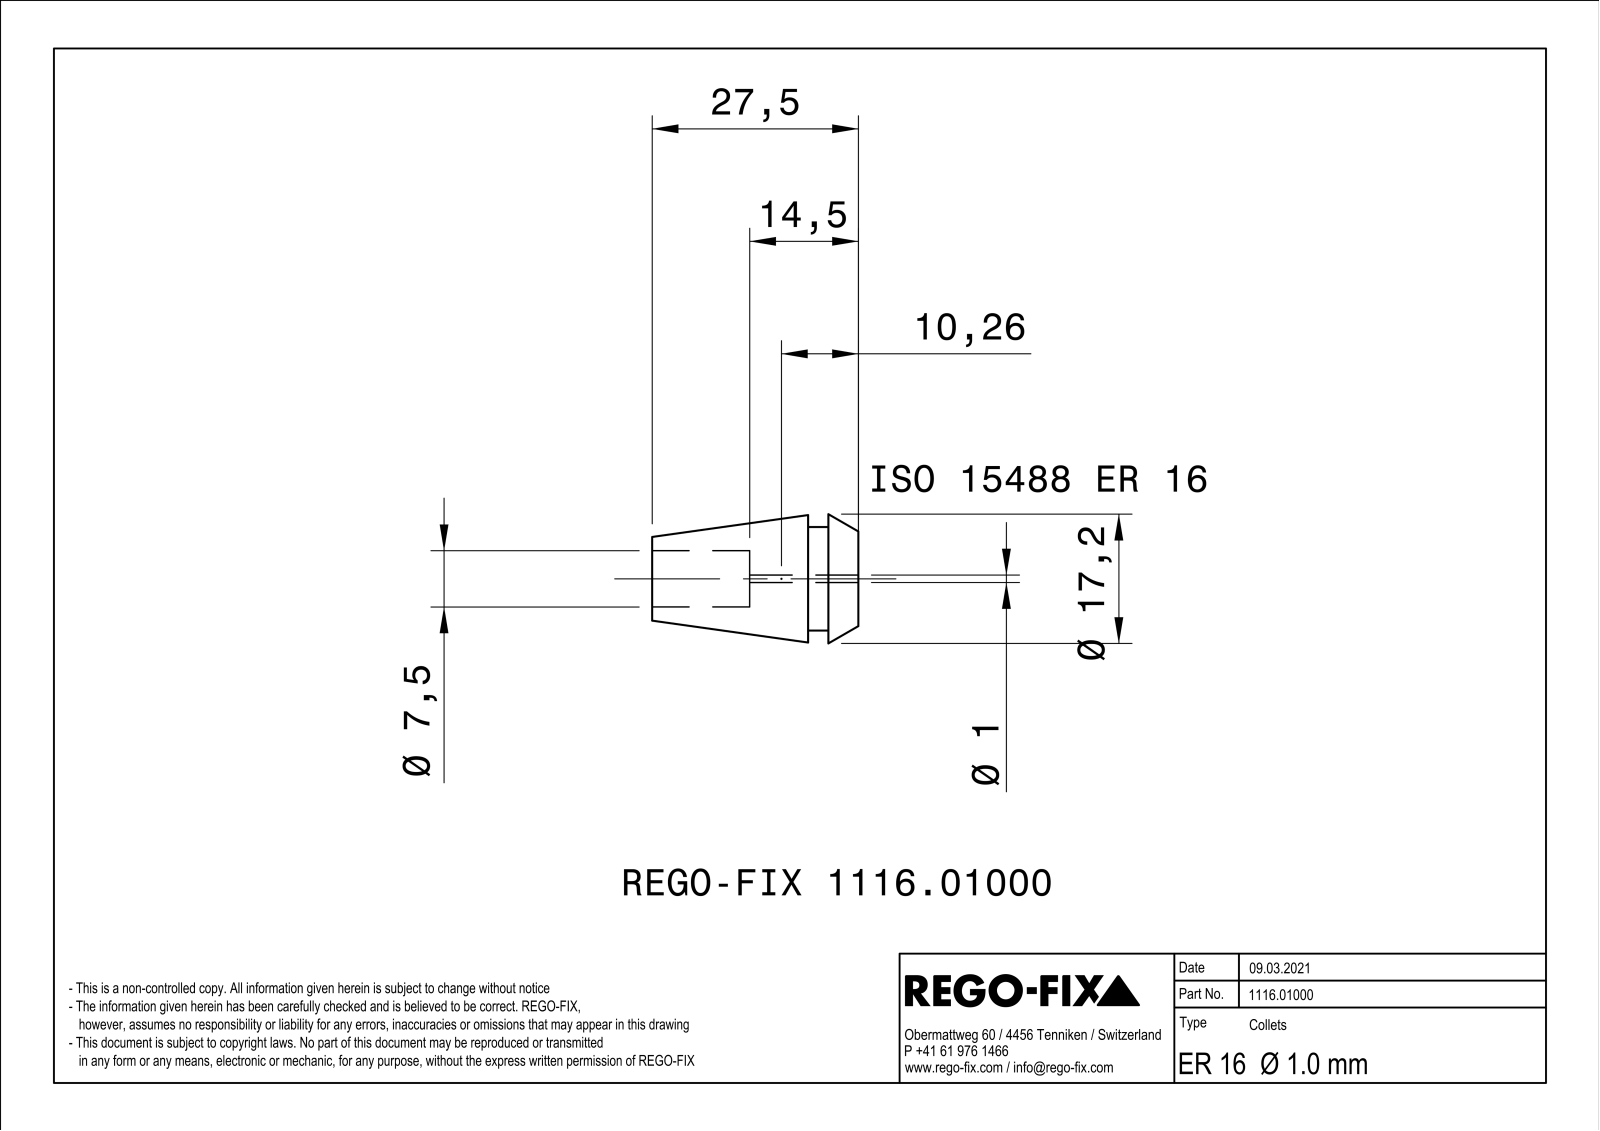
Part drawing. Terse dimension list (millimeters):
name: NOCUT
written by: SIEMENS PLM Software Solid Edge ST10 (AUTOMOTIVE_DESIGN)
unit: mm
bodies: 1 solid, 224 faces (108 planar, 28 cylindrical, 88 other)
size: 27.5 × 17.24 × 17.24
volume: 3 049 mm³; area: 5 087 mm²
holes: 1× ⌀7.5
bosses: 1× ⌀13.8
rounds: 1× R0.5
face distances: 0.46, 0.44, 0.45, 4, 6.7, 2.7, 3.27, 3.28, 3.72, 3.73
